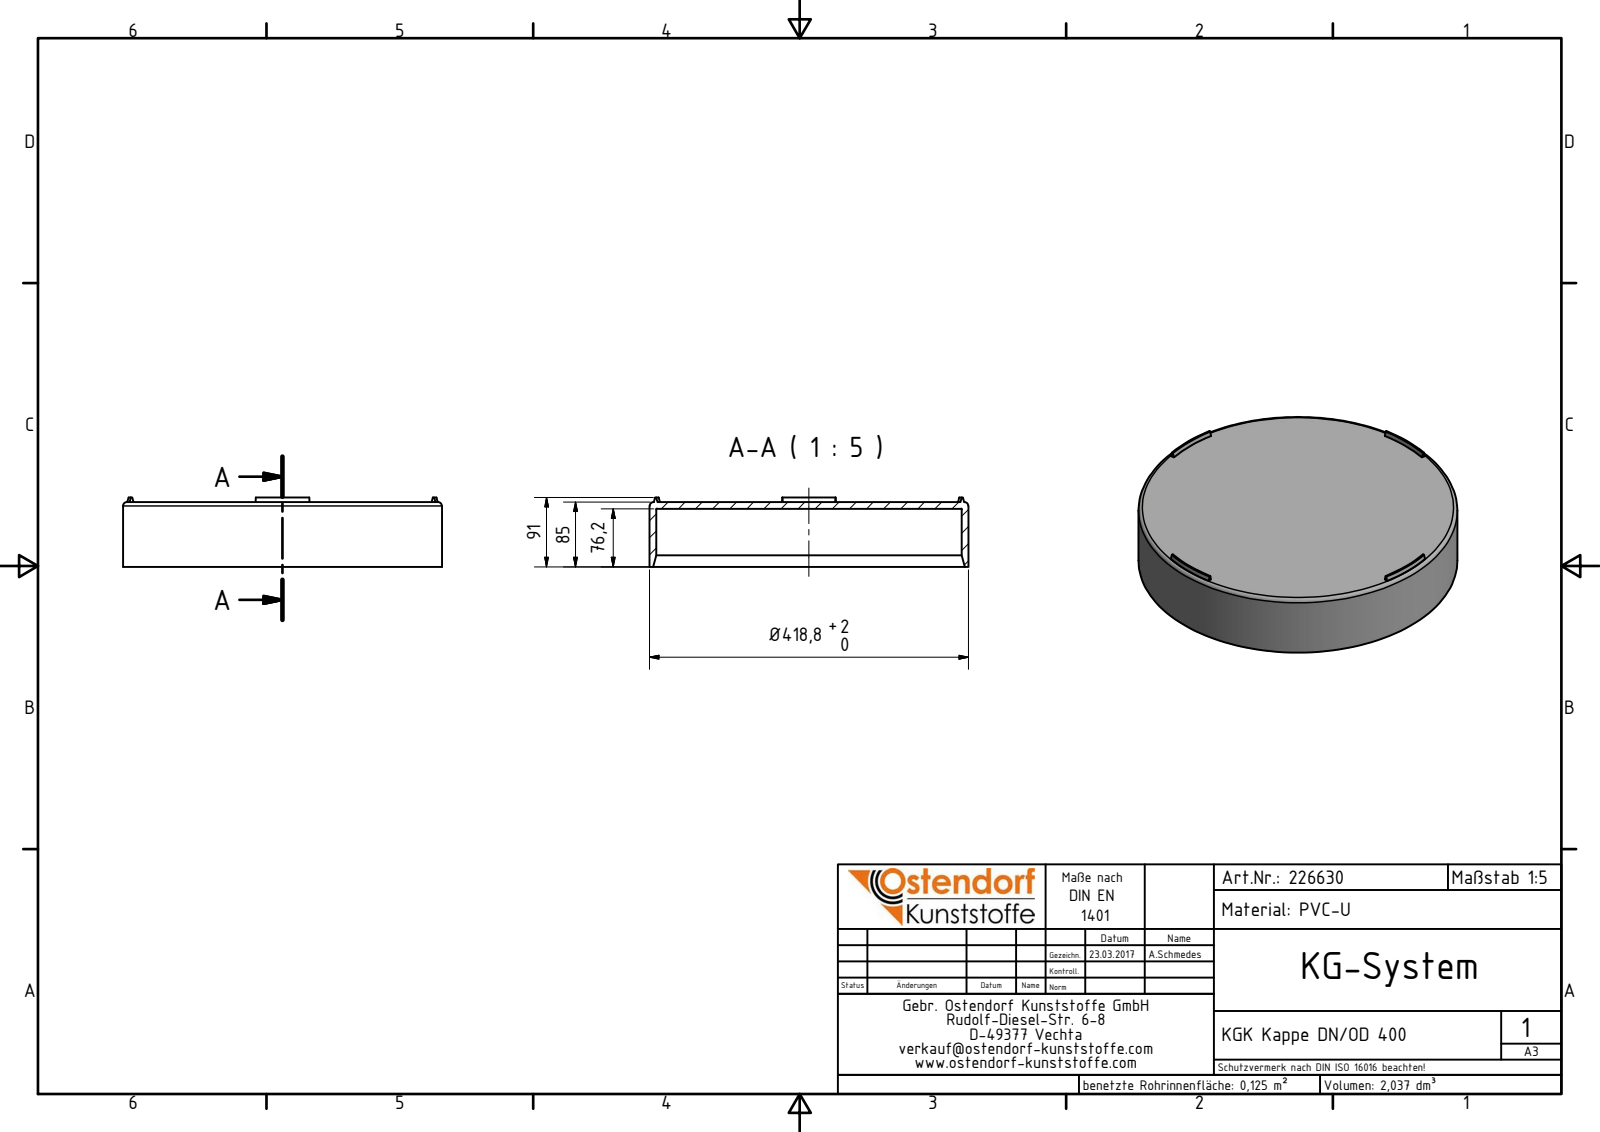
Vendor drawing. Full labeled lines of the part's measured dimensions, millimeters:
Part name (STEP PRODUCT): 226630 KGK Kappe DN_OD 400
STEP written by: Autodesk Inventor 2016 (AUTOMOTIVE_DESIGN)
Units: millimetres
Bodies: 1 solid, 28 faces (15 planar, 0 cylindrical, 13 other)
Overall size (bounding box): 418.8 × 418.8 × 91
Volume: 2 037 000 mm³ · Surface area: 478 453 mm²
Main face-to-face distances: 8.8, 76.2, 85, 91, 14.8, 6
